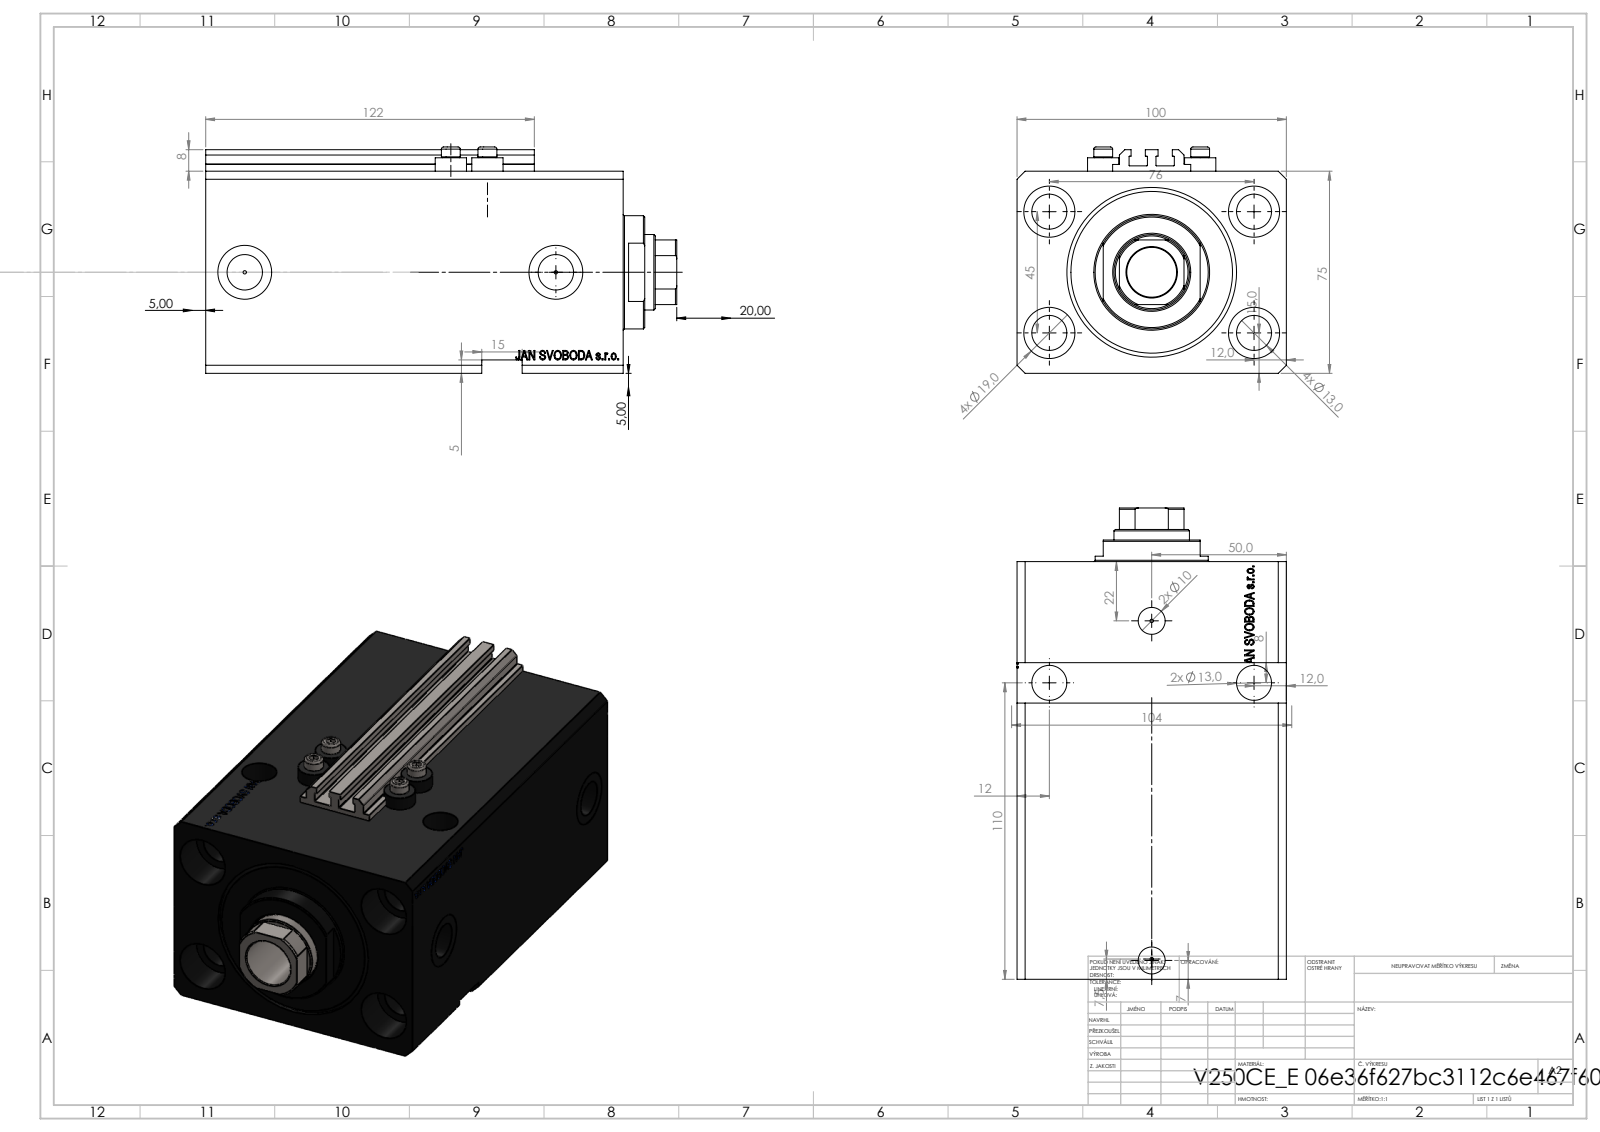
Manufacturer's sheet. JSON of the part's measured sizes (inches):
{"part_name": "V250CE_E_Body; ALLEN BOLT V250CE; V250CE_VC_E; V250CE_C_VCP", "step_written_by": "SolidWorks 2019 (CONFIG_CONTROL_DESIGN)", "units": "inches", "bodies": {"solids": 8, "faces": 1124, "planar": 539, "cylindrical": 158, "other": 427}, "overall_size": [6.89, 3.937, 3.307], "volume_in3": 57.18, "surface_area_in2": 274.5, "round_holes": [[0.512, 8], [0.049, 4], [0.157, 4], [0.748, 4], [0.394, 2], [0.518, 2], [0.787, 2], [0.728, 1], [1.102, 1], [1.969, 1], [2.48, 1]], "round_bosses_or_shafts": [[0.457, 4], [0.276, 4], [1.654, 1]], "partial_cylinders_radius": [[0.008, 10], [0.531, 1]], "face_to_face_distances": [2.953, 3.937, 6.102, 0.787, 0.469, 5.634, 5.315, 4.846, 0.512, 0.315], "hole_center_spacings": [1.739, 2.992, 0.535, 0.816, 1.086, 1.324, 1.417, 1.515]}
